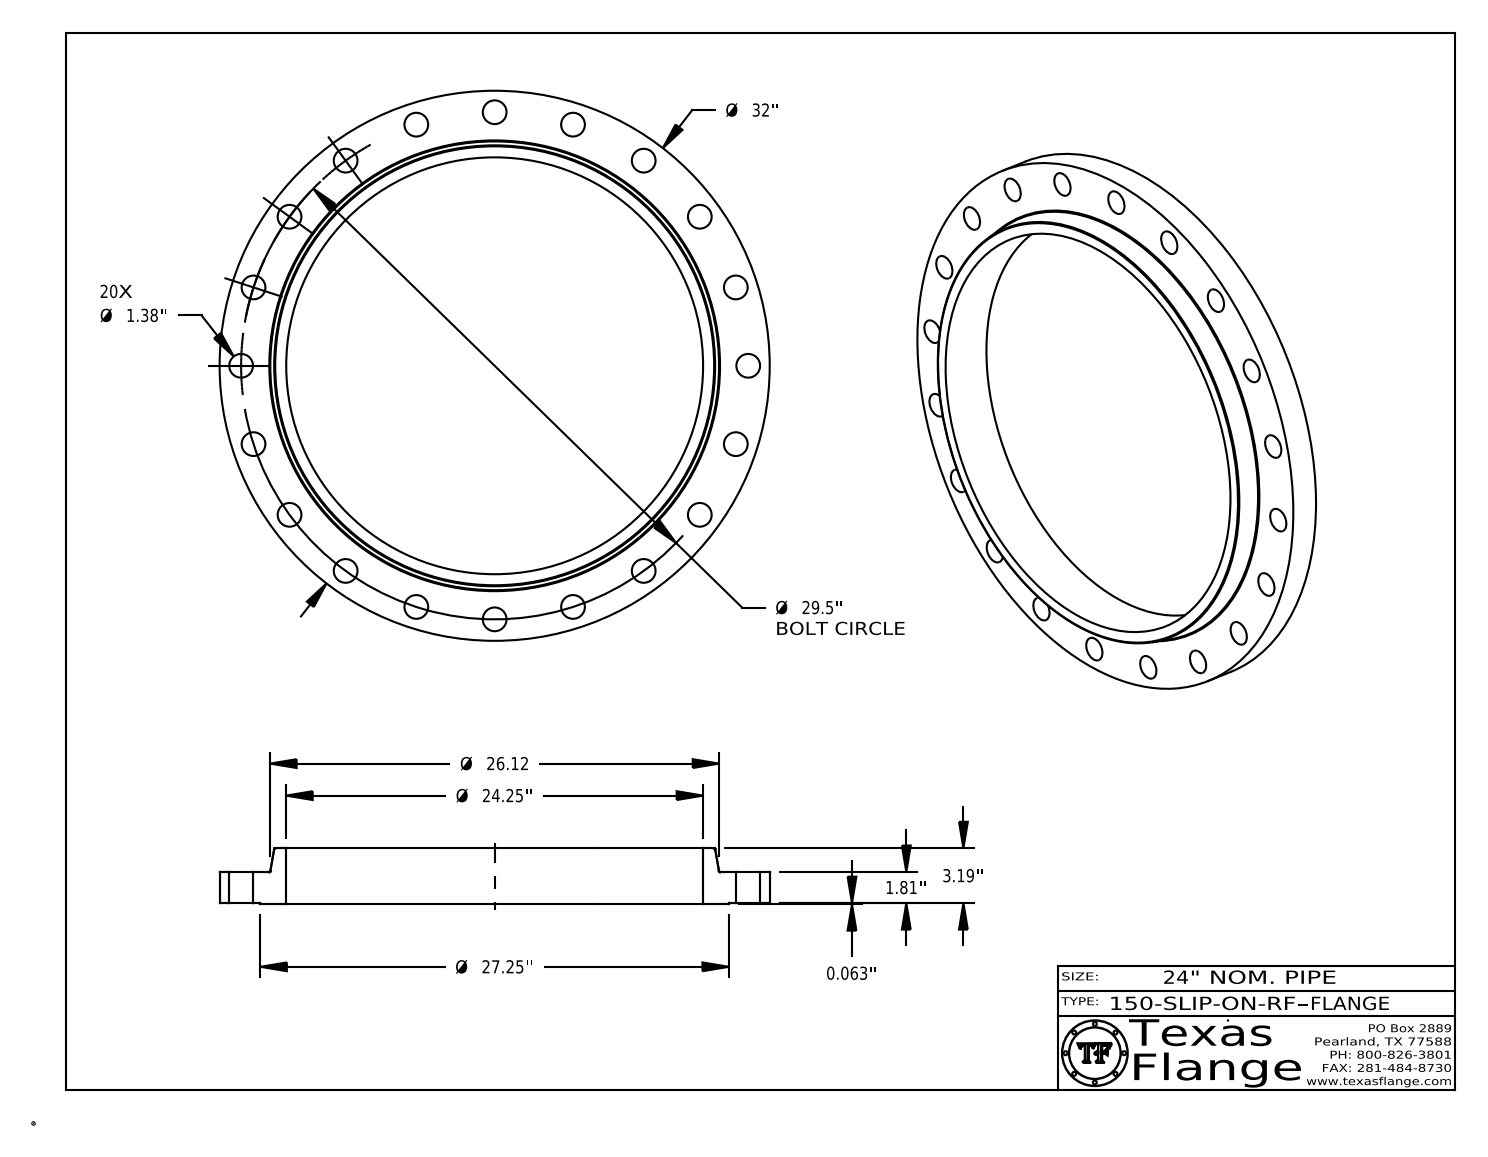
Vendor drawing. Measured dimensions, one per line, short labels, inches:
name: 150-SLIP-ON-RF
written by: CATIA V5 STEP AP214 (AUTOMOTIVE_DESIGN)
unit: in
bodies: 1 solid, 441 faces (369 planar, 66 cylindrical, 6 other)
size: 32 × 32 × 3.253
volume: 661.6 in³; area: 1 308 in²
holes: 20× ⌀1.38, 1× ⌀0.495, 1× ⌀24.25
bosses: 8× ⌀0.03, 1× ⌀32, 1× ⌀27.25, 1× ⌀0.39
face distances: 1.81, 0.063, 1.872, 3.253, 3.19, 1.38, 1.857, 1.795, 0.015, 1.395
hole spacings: 14.75, 29.137, 4.615, 17.34, 20.859, 23.866, 26.285, 9.116
